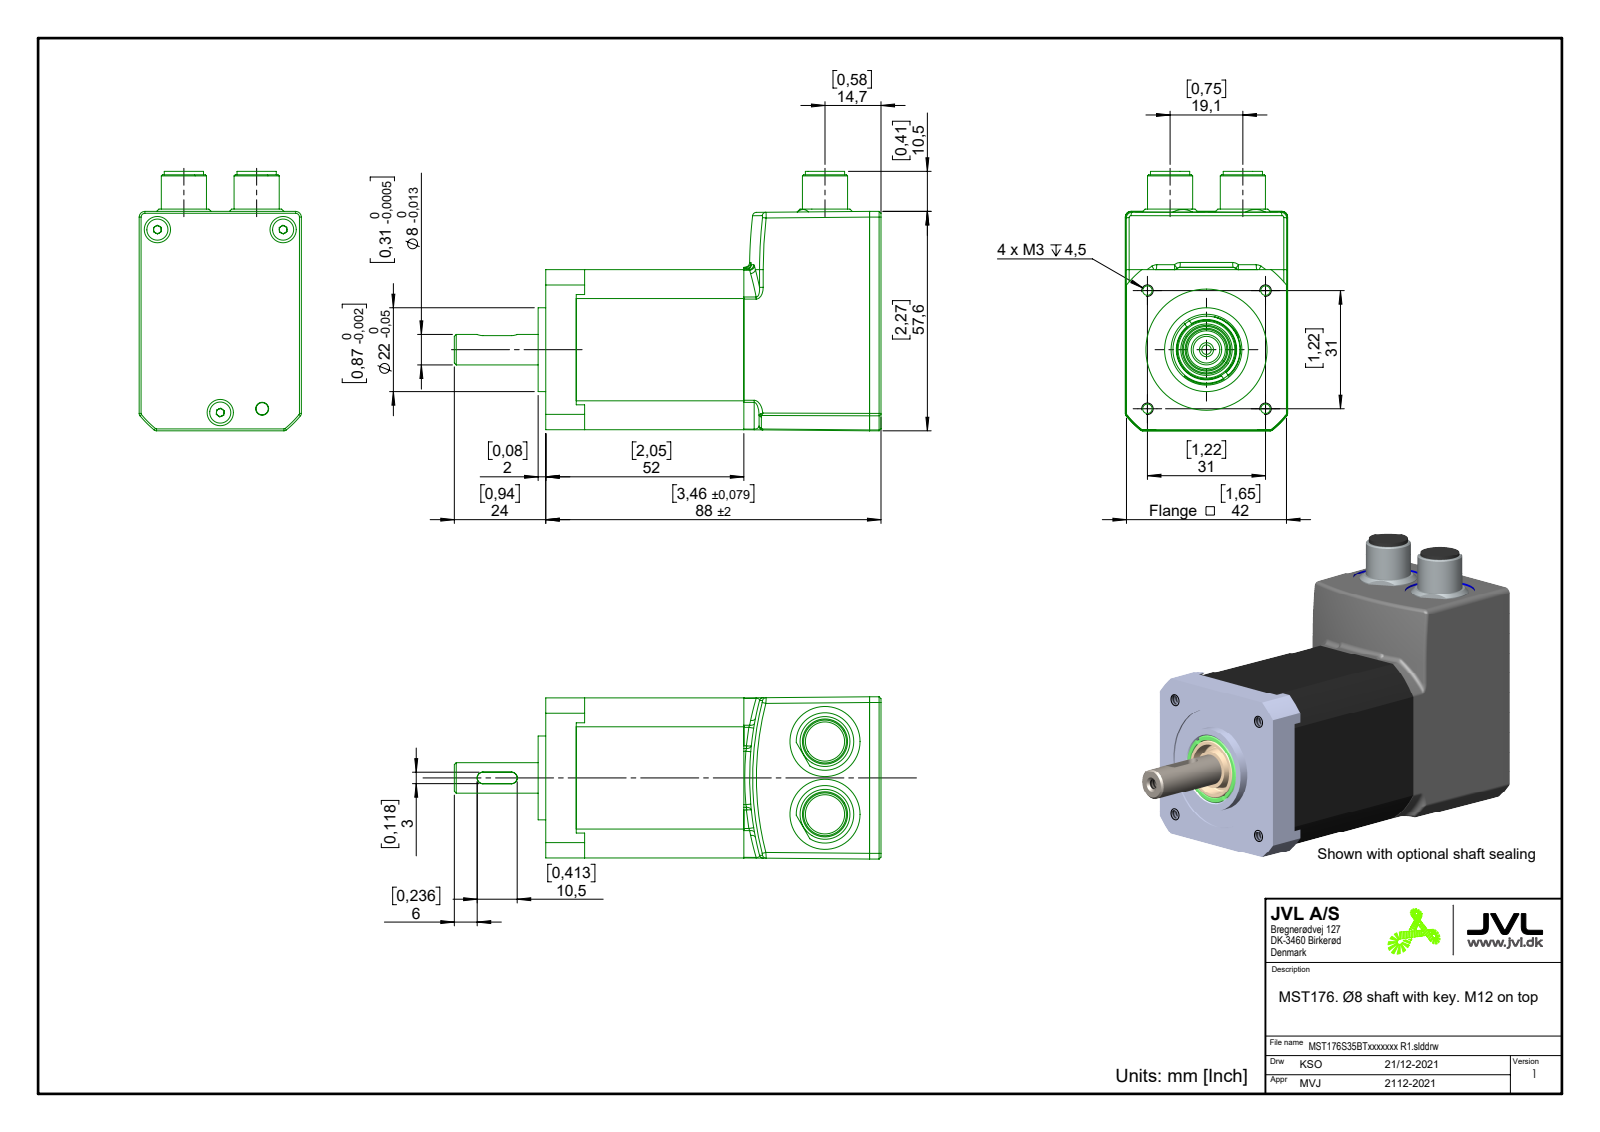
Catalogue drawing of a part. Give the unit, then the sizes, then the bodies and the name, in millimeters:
Units: millimetres
Overall size (bounding box): 112 × 68.08 × 42.58
Round holes (diameter × count): ⌀2.5 ×5, ⌀3.3 ×3, ⌀18.4 ×2, ⌀2.8 ×1, ⌀3.4 ×1, ⌀9 ×1, ⌀31.8 ×1
Round bosses / shafts (diameter × count): ⌀5.54 ×3, ⌀3 ×3, ⌀15.1 ×2, ⌀11.85 ×2, ⌀10.3 ×2, ⌀22 ×1, ⌀15.5 ×1, ⌀13.9 ×1
Partial cylindrical surfaces — rounded edges, fillets, slot ends (radius × count): R1 ×13, R1.5 ×4, R8.8 ×1, R24.92 ×1, R25.5 ×1, R27 ×1, R27.29 ×1, R80 ×1
Main face-to-face distances: 42, 88, 2, 87.5, 0.5, 42.29, 1.5, 86, 2.5, 4
Hole centre spacings: 21.92, 31, 35.56, 15.53, 16.03, 35.78, 43.84, 47.01
Volume: 175 501 mm³ · Surface area: 23 226 mm²
Bodies: 5 solids, 335 faces (136 planar, 73 cylindrical, 126 other)
Part name (STEP PRODUCT): MST176S35BTxxxxxxx
STEP written by: SolidWorks 2020 (AUTOMOTIVE_DESIGN)
